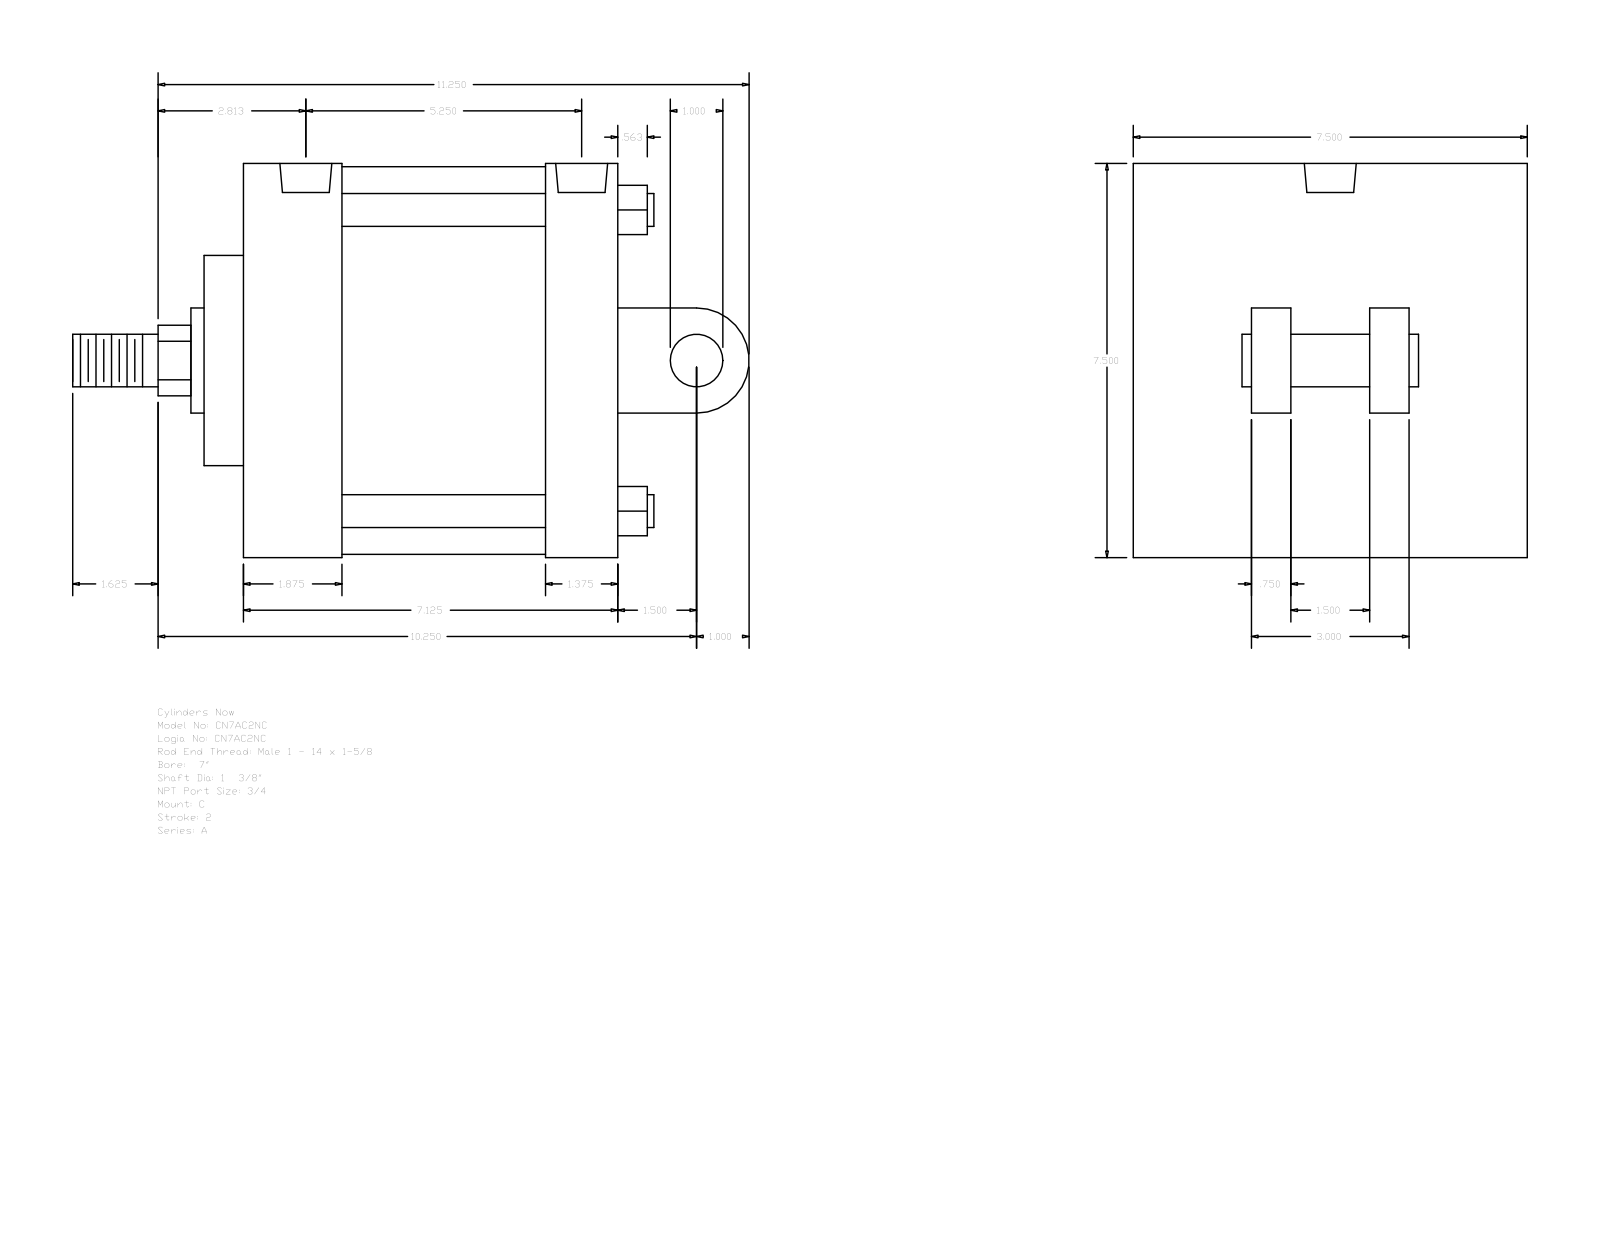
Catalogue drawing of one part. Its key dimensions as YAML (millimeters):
part_name: "A_C__0700_1.375"
step_written_by: "GSSL Pune (CONFIG_CONTROL_DESIGN)"
units: millimeters
bodies: {solids: 0, faces: 104, planar: 75, cylindrical: 29, other: 0}
overall_size: [327.02, 190.5, 190.5]
round_holes:
  - {diameter: 15.08, count: 4}
  - {diameter: 25.12, count: 2}
round_bosses_or_shafts:
  - {diameter: 15.88, count: 4}
  - {diameter: 25.4, count: 2}
  - {diameter: 187.32, count: 1}
  - {diameter: 50.8, count: 1}
  - {diameter: 34.92, count: 1}
partial_cylinders:
  - {radius: 17.06, count: 1}
  - {radius: 25.4, count: 1}
face_to_face_distances: [190.5, 180.98, 146.05, 133.35, 76.2, 57.15, 19.04, 200.02, 66.67, 47.63]
hole_center_spacings: [5.56, 122.23, 127.79, 133.35]
